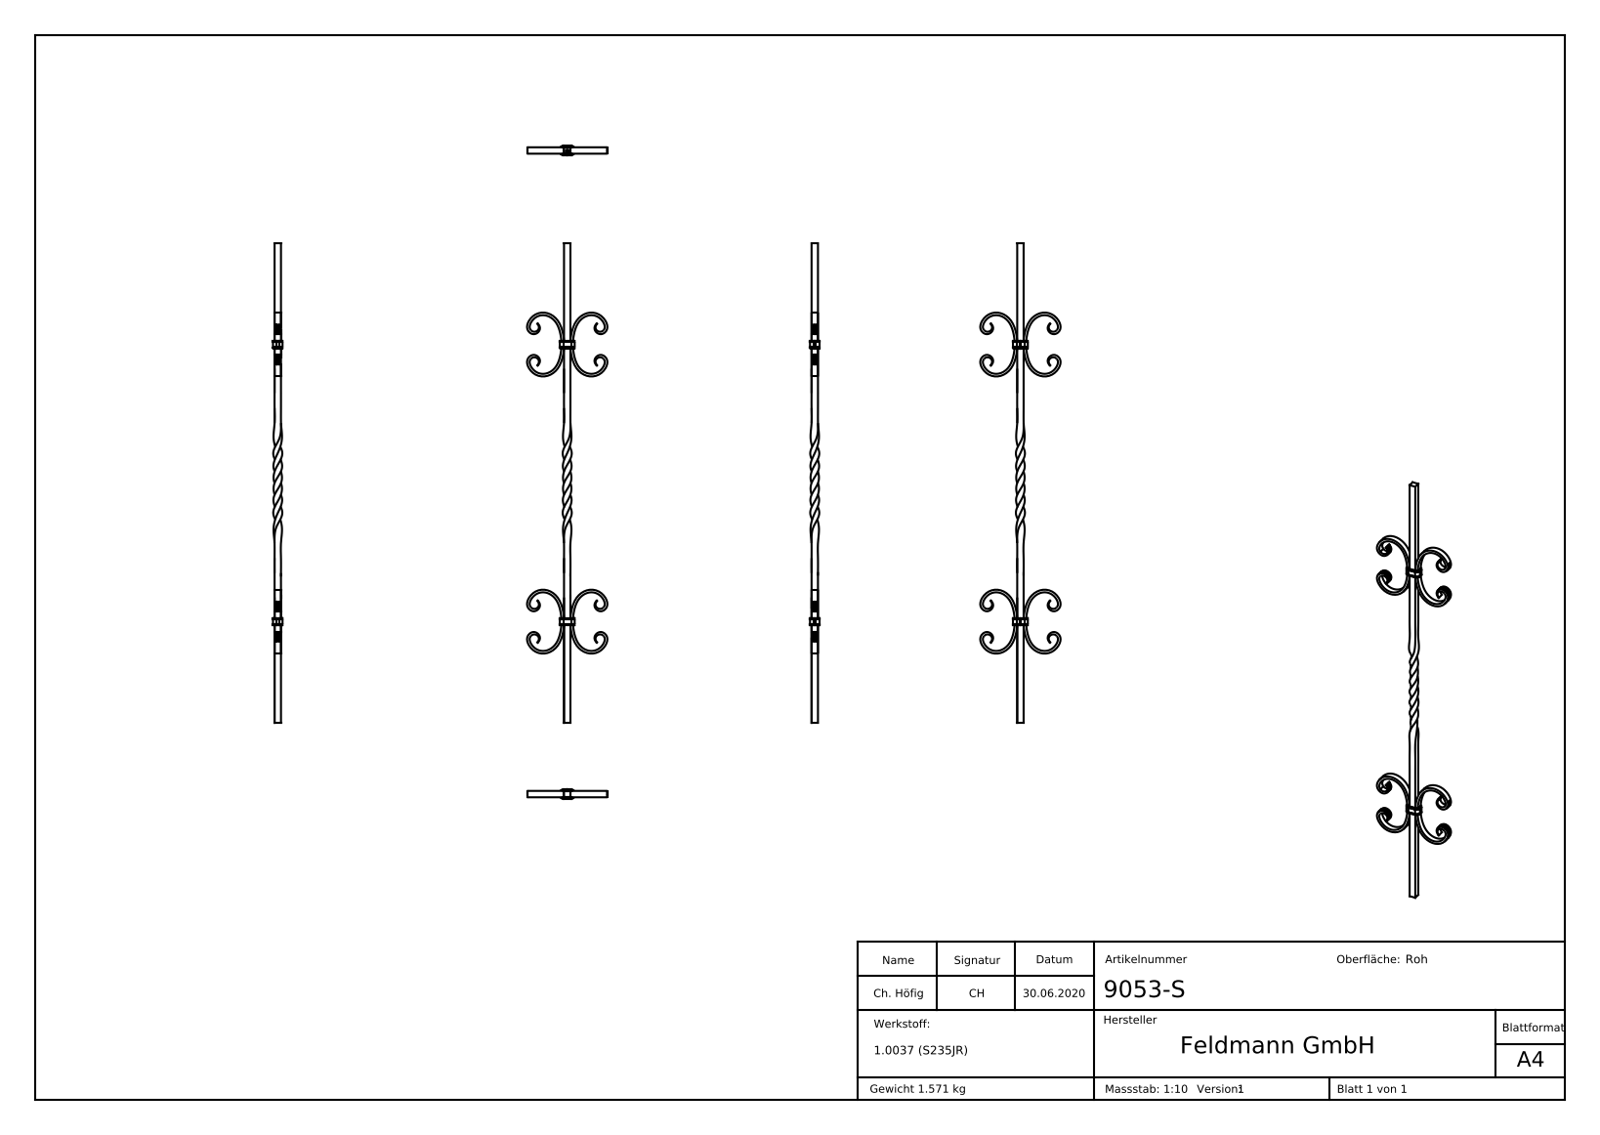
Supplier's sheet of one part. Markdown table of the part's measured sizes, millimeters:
| quantity | value |
| --- | --- |
| part name | 9053-S Teil2; 9053-S Teil3; 9053-S Teil1; 9053-S |
| STEP written by | SolidWorks 2018 (CONFIG_CONTROL_DESIGN) |
| units | millimeters |
| bodies | 7 solids, 574 faces (219 planar, 120 cylindrical, 235 other) |
| overall size | 900 × 150.84 × 18.07 |
| volume | 201 953 mm³ |
| surface area | 90 982 mm² |
| partial cylindrical surfaces (radius × count) | 1 × 32, 0.25 × 16, 4 × 8, 25.25 × 8, 3.9 × 4, 6.9 × 4 |
| main face-to-face distances | 12, 12.07, 520, 2, 900, 197, 703, 183, 717, 14 |
